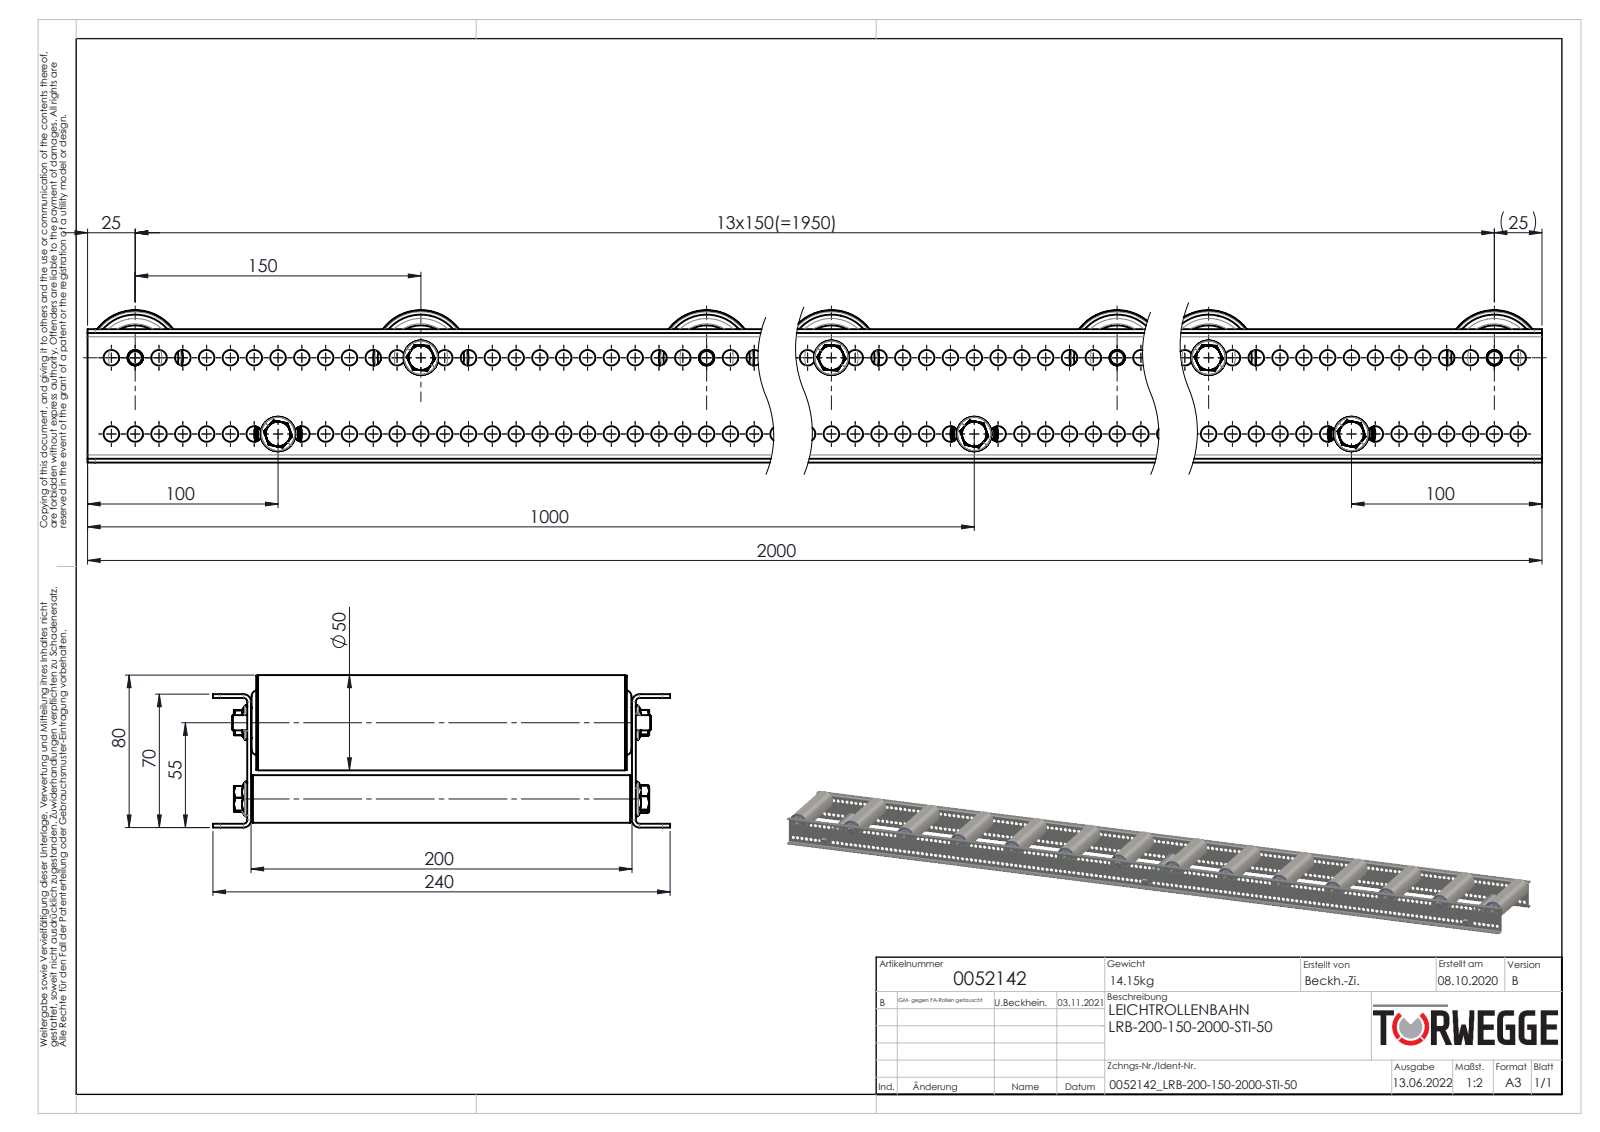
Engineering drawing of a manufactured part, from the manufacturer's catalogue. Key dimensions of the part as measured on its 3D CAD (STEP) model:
Part name (STEP PRODUCT): TRG-50x1,5-STI-A12-IGM8-EL=KFG_0022776TWG_TRG-50x1,5-STI-A12-IGM8-EL=200; 0039780-Achse-ST-Ø12-KFG_IGM8-AL=200-TRG; 0039771_Tragrollenrohr-Ø50x1,5STI_KFG_EL200; Traversen_KFG_L200 (+8 more)
STEP written by: SolidWorks 2020 (AUTOMOTIVE_DESIGN)
Units: millimetres
Bodies: 350 solids, 6934 faces (1320 planar, 2752 cylindrical, 2862 other)
Overall size (bounding box): 2000 × 240 × 80
Volume: 1 949 000 mm³ · Surface area: 2 239 000 mm²
Round holes (diameter × count): ⌀8.2 ×318, ⌀17.1 ×14, ⌀18.5 ×14, ⌀27.7 ×14, ⌀45.3 ×14, ⌀47 ×14, ⌀7.6 ×11, ⌀6.8 ×6, ⌀12 ×3, ⌀12.2 ×3, ⌀19.2 ×3, ⌀21 ×3
Round bosses / shafts (diameter × count): ⌀8 ×17, ⌀50 ×14, ⌀49.5 ×14, ⌀47.3 ×14, ⌀29.7 ×14, ⌀27.4 ×14, ⌀27.3 ×14, ⌀16 ×14
Partial cylindrical surfaces — rounded edges, fillets, slot ends (radius × count): R0.6 ×22, R0.75 ×22, R2.45 ×22, R2.5 ×12, R4.87 ×11, R7 ×11, R4 ×8, R2 ×4
Main face-to-face distances: 2, 202, 68, 200, 204, 70, 66, 18, 20, 220
Hole centre spacings: 12.5, 25, 37.5, 50, 62.5, 75, 87.5, 100
